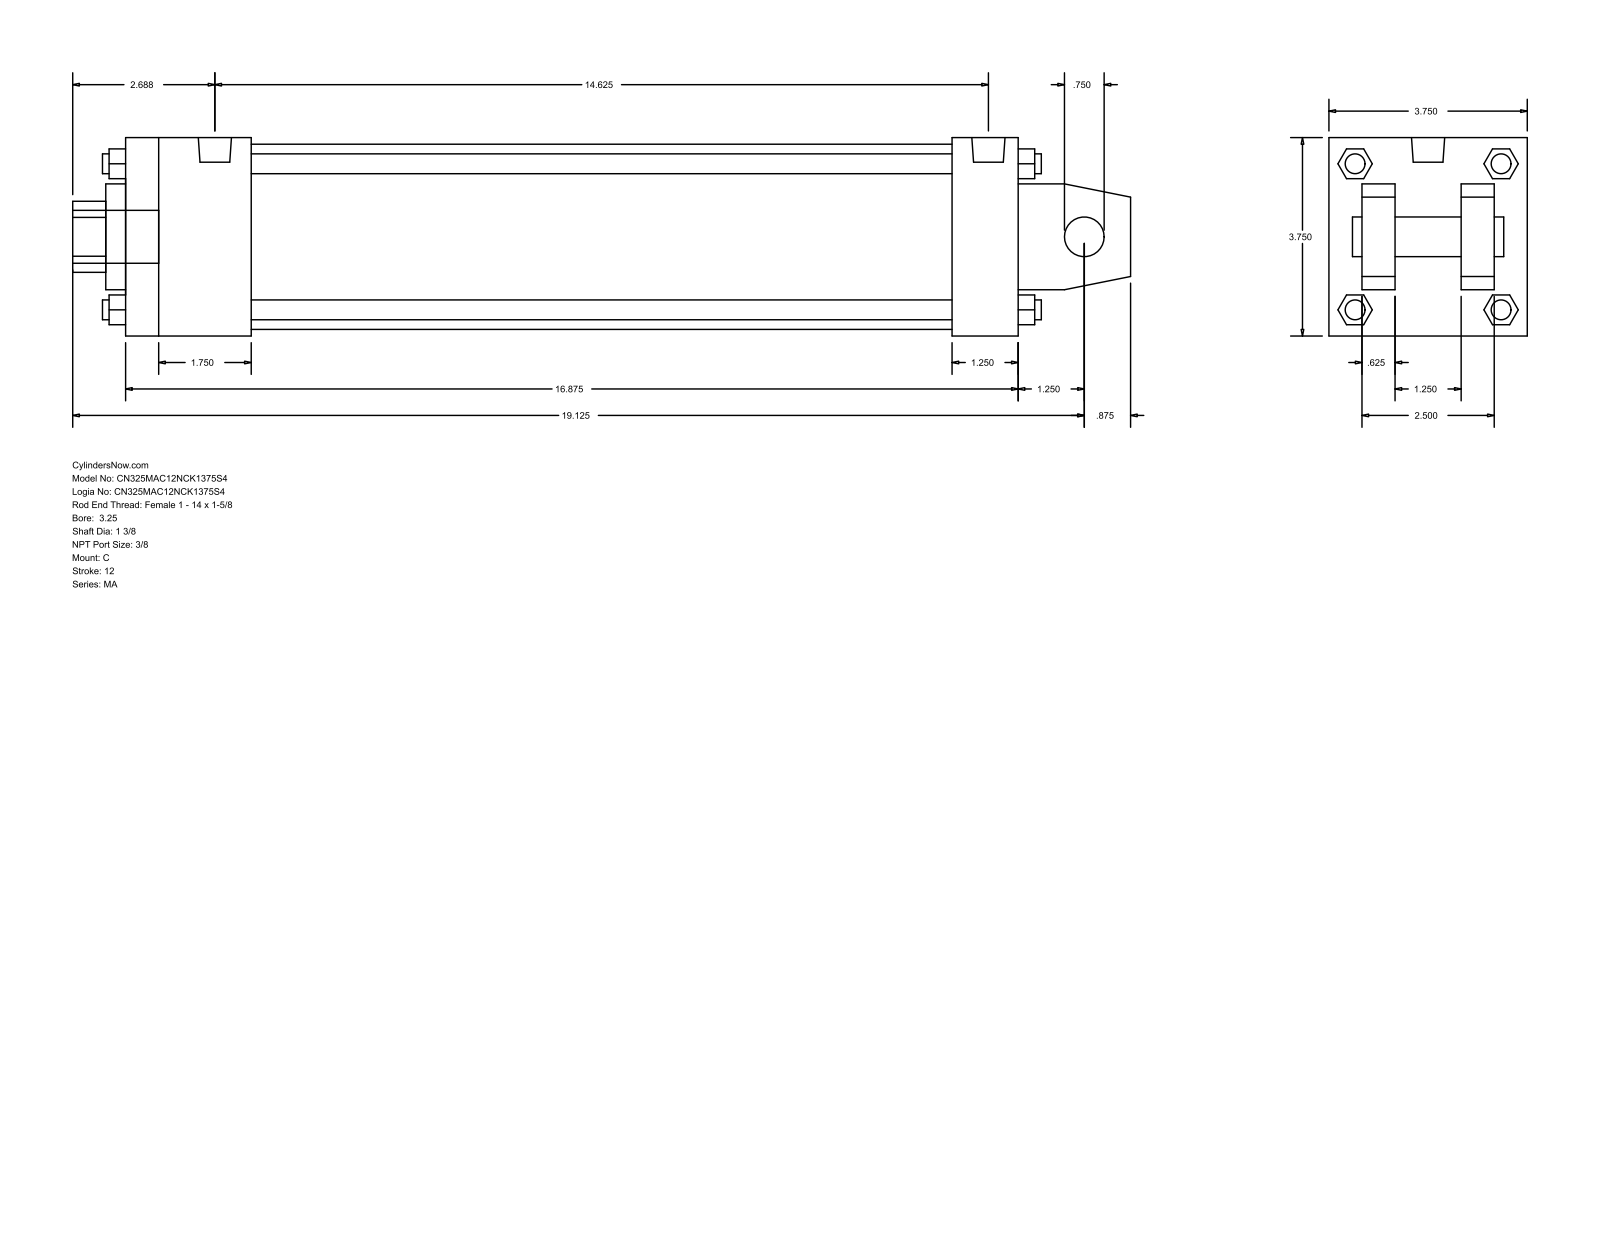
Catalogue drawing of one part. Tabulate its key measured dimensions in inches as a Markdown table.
| quantity | value |
| --- | --- |
| part name | MA_C__0325_1.375 |
| STEP written by | GSSL Pune (CONFIG_CONTROL_DESIGN) |
| units | inches |
| bodies | 0 solids, 139 faces (108 planar, 31 cylindrical, 0 other) |
| overall size | 20 × 3.75 × 3.75 |
| round holes (diameter × count) | 0.75 × 1, 1.375 × 1, 2 × 1, 3.5 × 1 |
| round bosses / shafts (diameter × count) | 0.437 × 4, 0.375 × 4, 0.627 × 2, 1 × 1 |
| partial cylindrical surfaces (radius × count) | 0.672 × 1 |
| main face-to-face distances | 3.75, 0.625, 2.5, 16.875, 1.25, 3.125, 1.875, 15.625, 1.25, 2.375 |
